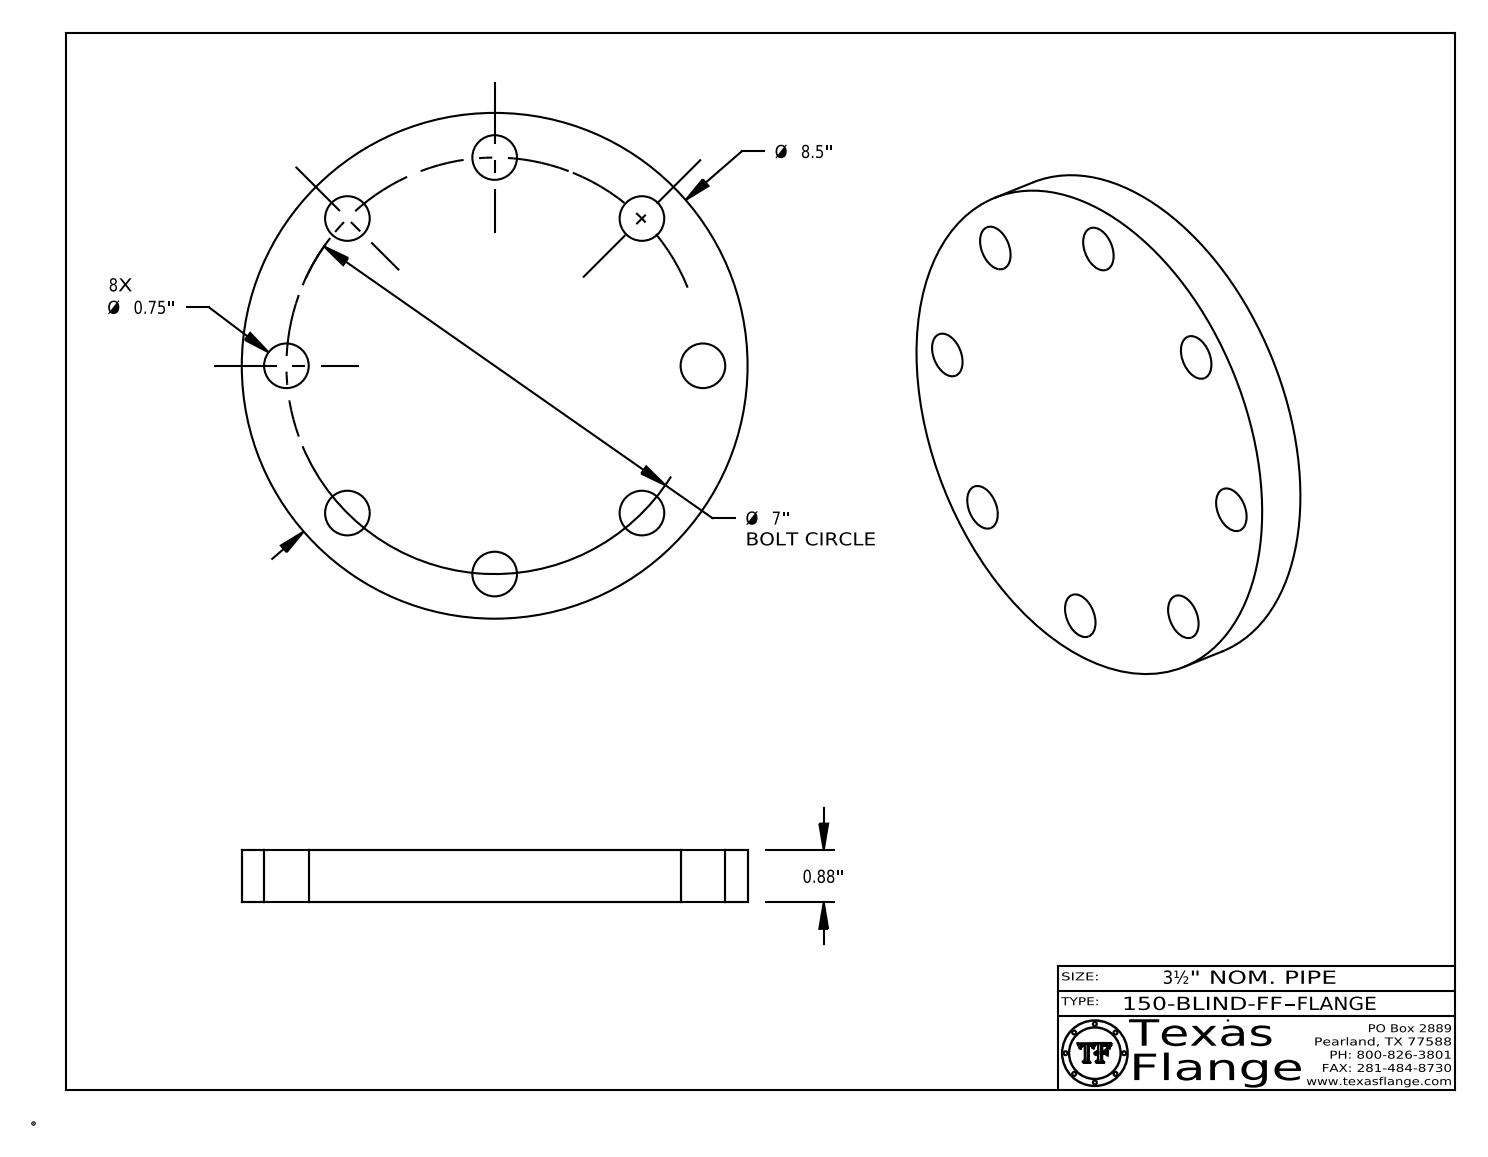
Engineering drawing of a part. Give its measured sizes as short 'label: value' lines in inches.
name: 150-BLIND-FF
written by: CATIA V5 STEP AP214 (AUTOMOTIVE_DESIGN)
unit: in
bodies: 1 solid, 405 faces (367 planar, 38 cylindrical, 0 other)
size: 8.5 × 8.5 × 0.88
volume: 46.82 in³; area: 146.6 in²
holes: 8× ⌀0.75, 1× ⌀0.495
bosses: 8× ⌀0.03, 1× ⌀8.5, 1× ⌀0.39
face distances: 0.88, 0.865, 0.015, 0.148, 0.145, 0.027, 0.122, 0.096, 0.101, 0.074
hole spacings: 2.679, 4.95, 6.467, 1.366, 3.889, 5.82, 6.865, 7
